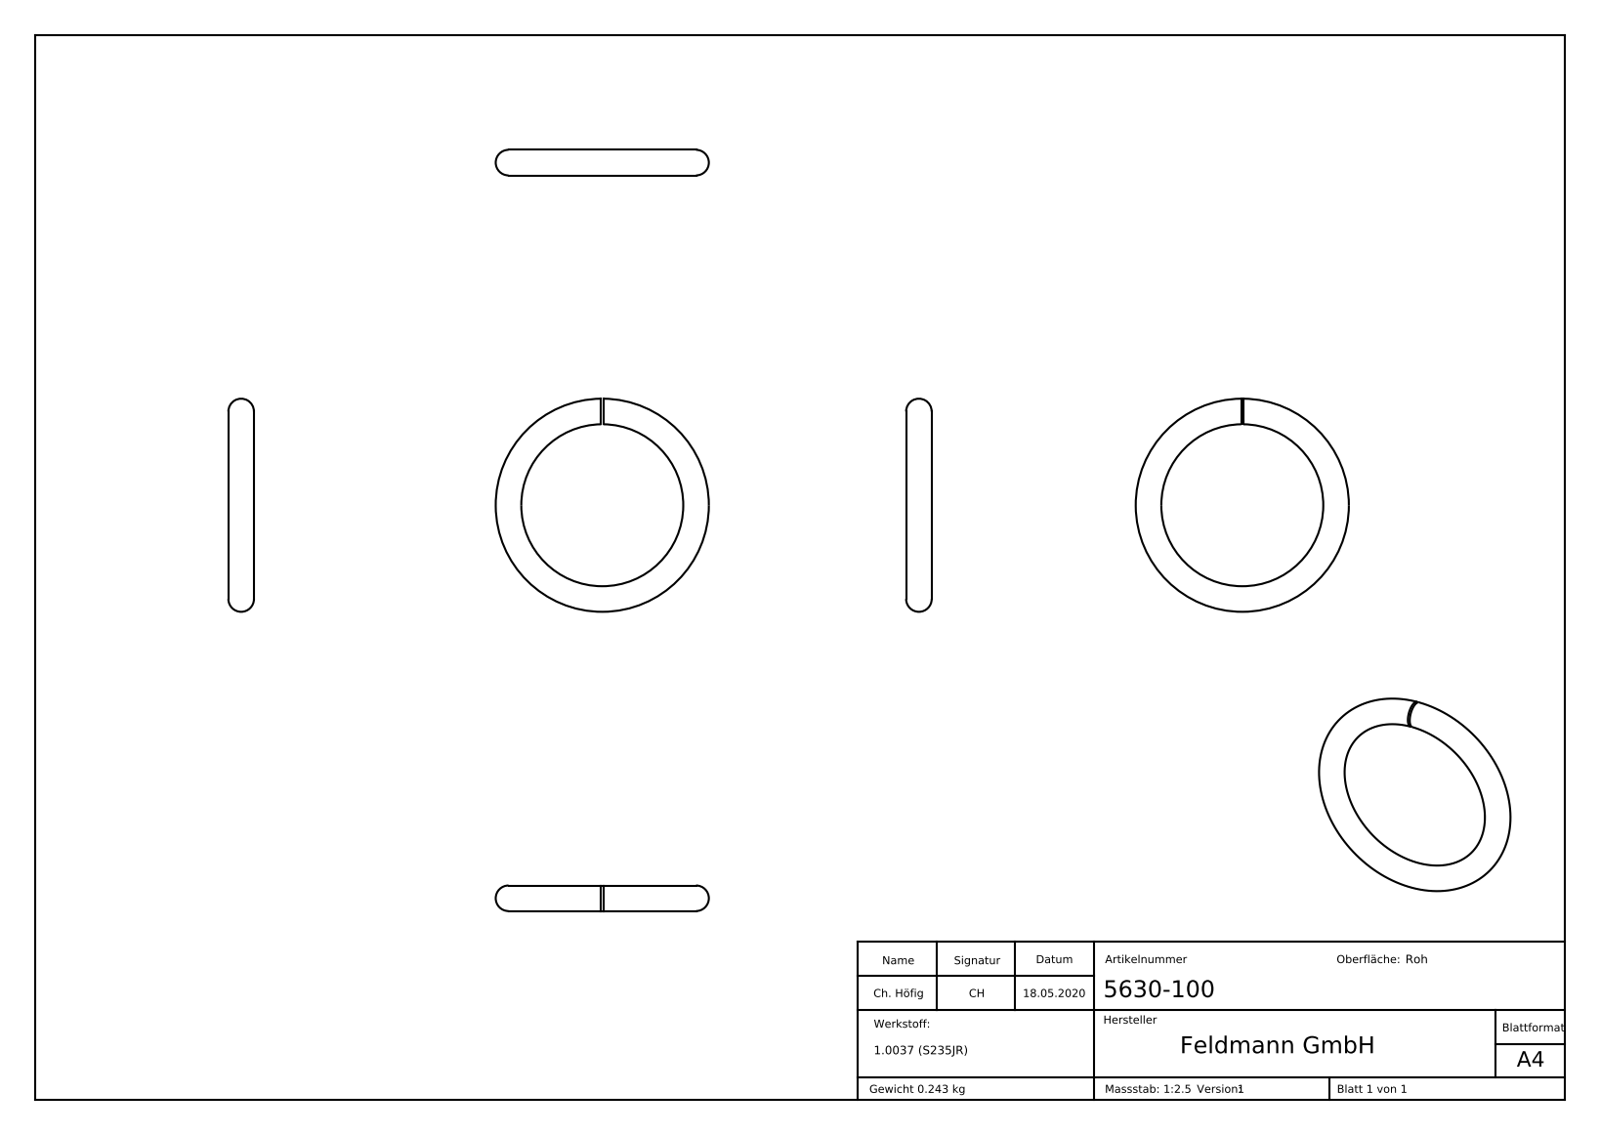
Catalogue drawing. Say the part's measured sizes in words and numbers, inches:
The part is named "5630-100". Its 3-D file was written by "SolidWorks 2015 (CONFIG_CONTROL_DESIGN)". It is 1 solid with 208 faces: 101 planar, 0 cylindrical and 107 other. Overall it measures 3.937 by 3.937 by 0.472 inches. Its volume is 1.901 cubic inches and its surface area 16.49 square inches. The main face-to-face distances are 0.039, 0.059, 0.02, 0.07, 0.083, 0.033, 0.096, 0.039, 0.109, 0.026.
